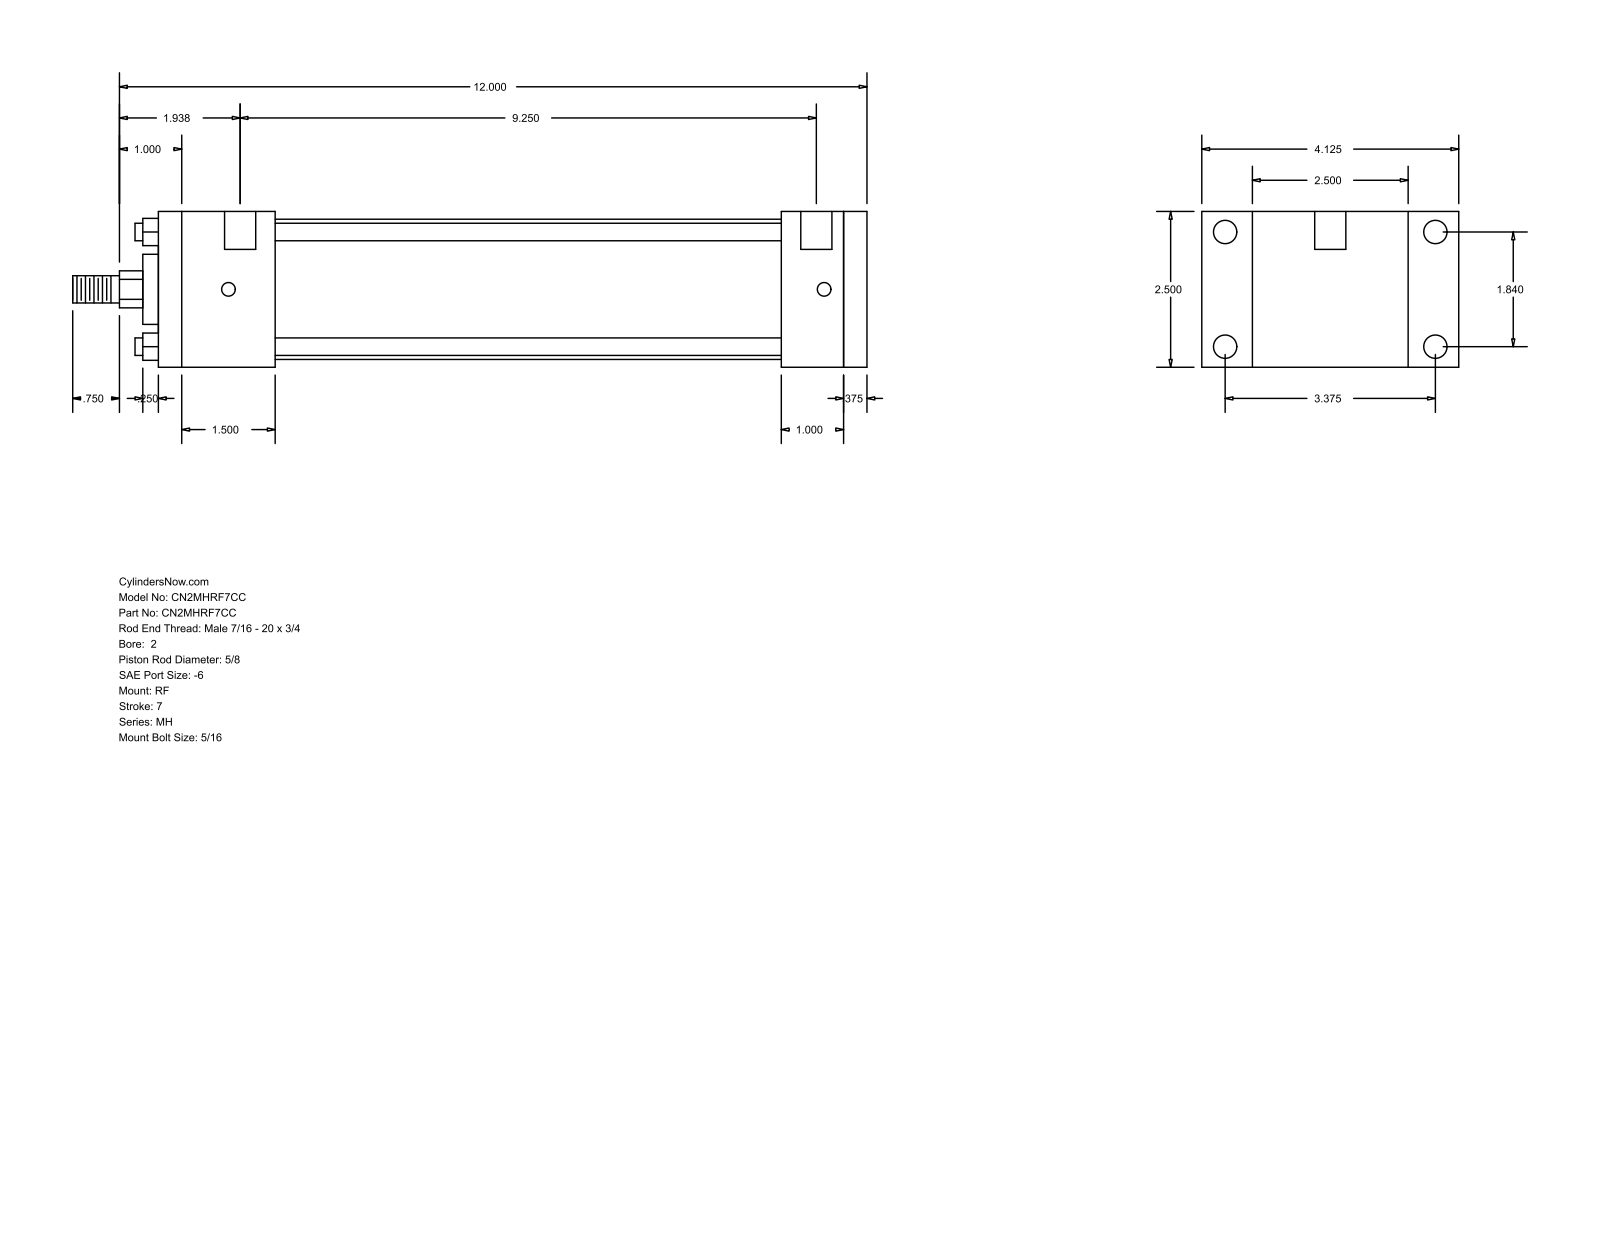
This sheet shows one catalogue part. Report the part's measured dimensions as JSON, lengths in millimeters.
{"part_name": "MH_RF__0200_0.625", "step_written_by": "GSSL Pune (CONFIG_CONTROL_DESIGN)", "units": "millimeters", "bodies": {"solids": 0, "faces": 92, "planar": 64, "cylindrical": 28, "other": 0}, "overall_size": [323.85, 104.78, 63.5], "round_holes": [[5.56, 4], [9.53, 4], [12.7, 2]], "round_bosses_or_shafts": [[7.14, 4], [57.15, 1], [28.57, 1], [15.88, 1], [11.11, 1]], "partial_cylinders_radius": [[7.54, 1]], "face_to_face_distances": [63.5, 288.92, 9.53, 279.39, 47.62, 254, 206.38, 231.77, 241.3, 25.39], "hole_center_spacings": [46.74, 85.72, 97.63, 242.89, 3.18, 4.76, 234.95, 238.13]}
